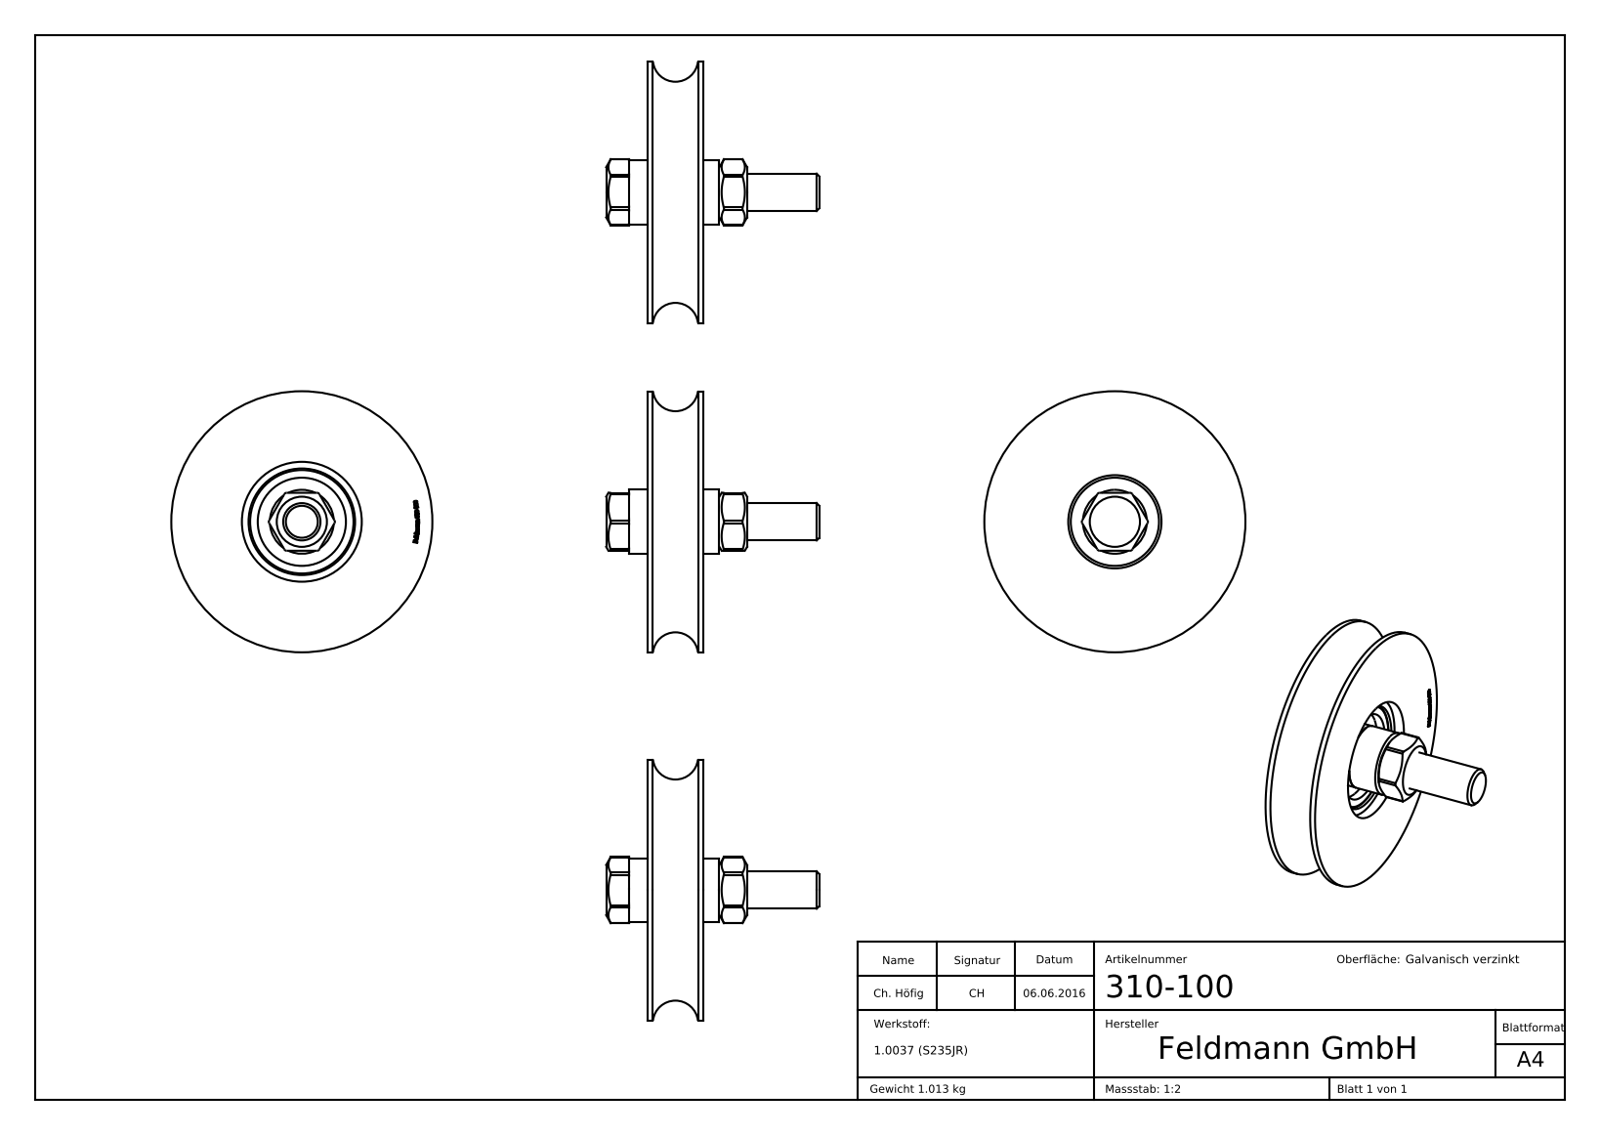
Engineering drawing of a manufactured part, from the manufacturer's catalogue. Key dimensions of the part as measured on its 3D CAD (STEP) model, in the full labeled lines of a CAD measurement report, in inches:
Part name (STEP PRODUCT): 310-100 Teil2; 310-100 Teil1; 310-100 Teil5_310-100 Teil5; radial ball bearing_68_din (+7 more)
STEP written by: SolidWorks 2018 (CONFIG_CONTROL_DESIGN)
Units: inches
Bodies: 6 solids, 256 faces (125 planar, 31 cylindrical, 100 other)
Overall size (bounding box): 3.858 × 3.858 × 3.15
Volume: 8.458 in³ · Surface area: 62.43 in²
Round holes (diameter × count): ⌀0.472 ×1, ⌀0.551 ×1, ⌀0.669 ×1, ⌀1.303 ×1, ⌀1.378 ×1, ⌀1.575 ×1, ⌀1.772 ×1
Round bosses / shafts (diameter × count): ⌀3.858 ×1, ⌀0.945 ×1, ⌀0.941 ×1, ⌀0.663 ×1
Partial cylindrical surfaces — rounded edges, fillets, slot ends (radius × count): R0.039 ×6
Main face-to-face distances: 0.827, 0.157, 0.669, 0.433, 0.906, 0.63, 0.197, 0.472, 0.276, 1.102
